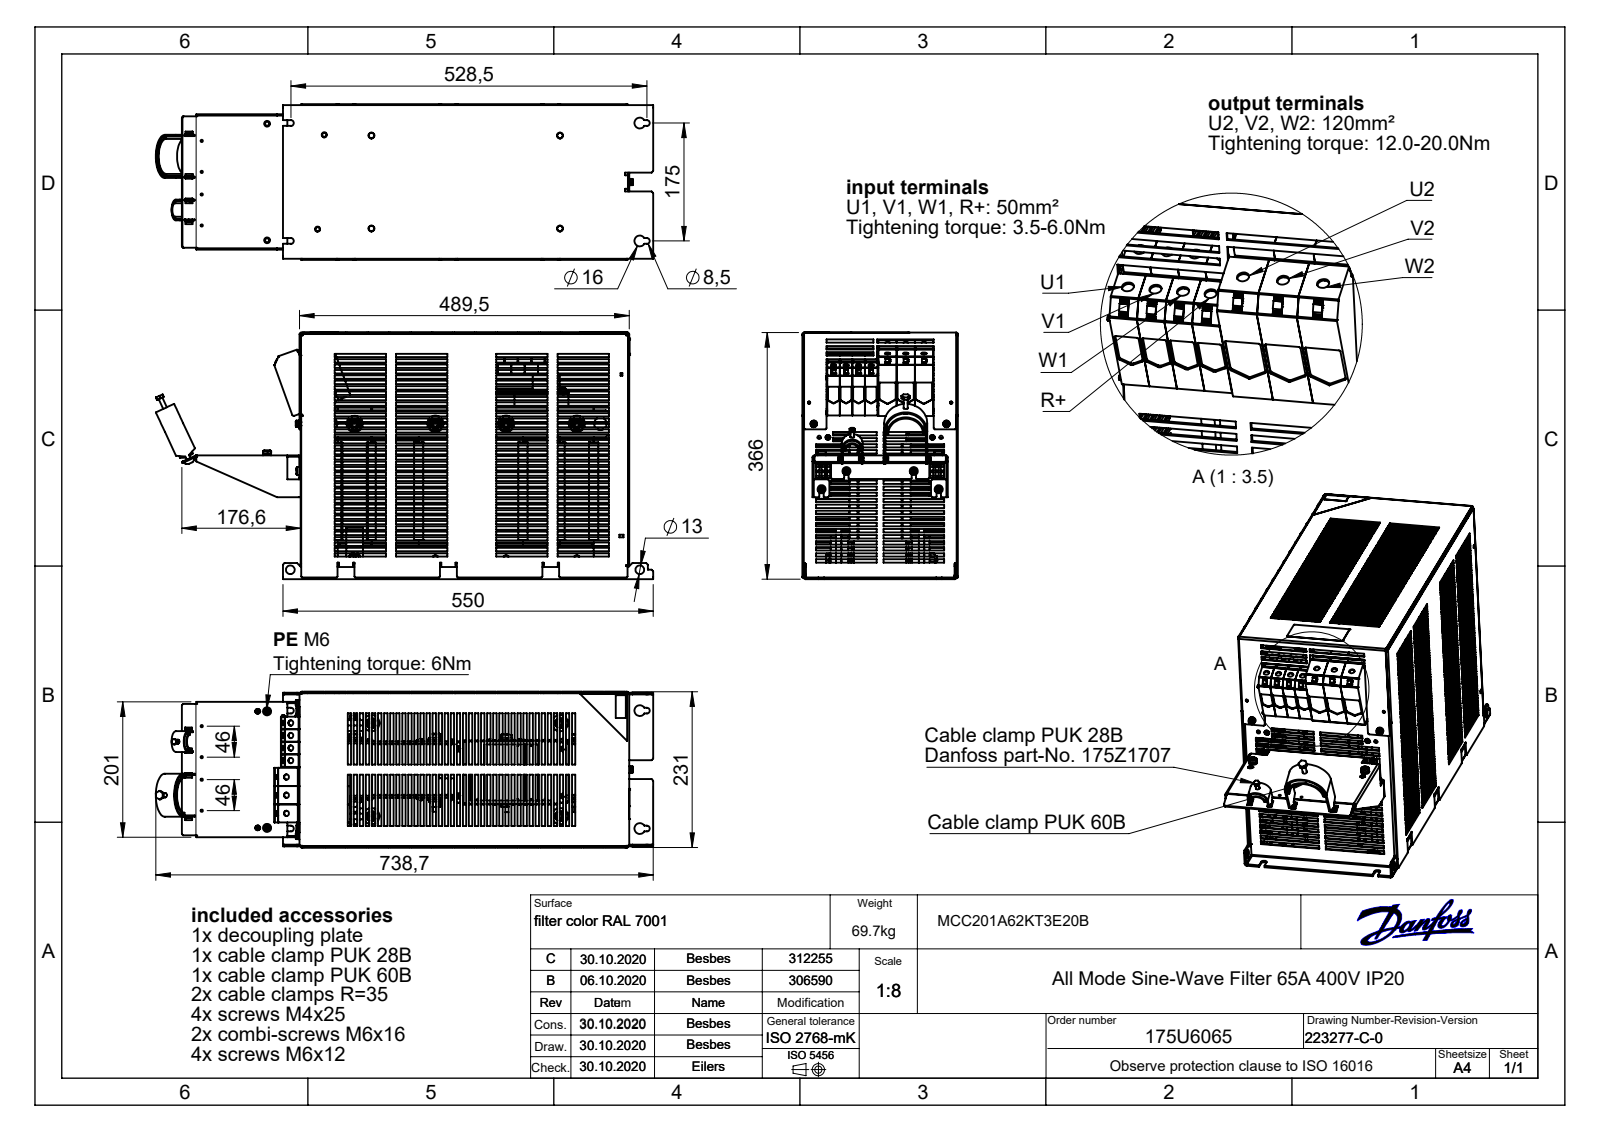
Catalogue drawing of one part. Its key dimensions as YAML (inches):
part_name: "200603 65A STEP; 139289; 128728; PEM Bolzen FH M6x15 10.9 vz_PEM Bolzen FH M6x15 10.9 vz (+8 more)"
step_written_by: "SolidWorks 2018 (AUTOMOTIVE_DESIGN)"
units: inches
bodies: {solids: 162, faces: 7219, planar: 5284, cylindrical: 1307, other: 628}
overall_size: [29.082, 14.413, 9.094]
volume: 790.9
surface_area: 5327
round_holes:
  - {diameter: 0.315, count: 23}
  - {diameter: 0.197, count: 14}
  - {diameter: 0.268, count: 12}
  - {diameter: 0.138, count: 10}
  - {diameter: 0.13, count: 8}
  - {diameter: 0.323, count: 8}
  - {diameter: 0.433, count: 8}
  - {diameter: 0.165, count: 7}
  - {diameter: 0.177, count: 7}
  - {diameter: 0.313, count: 7}
  - {diameter: 0.512, count: 7}
  - {diameter: 0.126, count: 6}
round_bosses_or_shafts:
  - {diameter: 0.039, count: 20}
  - {diameter: 0.315, count: 15}
  - {diameter: 0.63, count: 12}
  - {diameter: 0.709, count: 8}
  - {diameter: 0.394, count: 8}
  - {diameter: 0.236, count: 7}
  - {diameter: 0.472, count: 6}
  - {diameter: 0.945, count: 5}
partial_cylinders:
  - {radius: 0.039, count: 84}
  - {radius: 0.012, count: 34}
  - {radius: 0.035, count: 28}
  - {radius: 0.217, count: 22}
  - {radius: 0.079, count: 20}
  - {radius: 0.118, count: 19}
  - {radius: 0.394, count: 19}
  - {radius: 0.276, count: 16}
face_to_face_distances: [0.059, 3.012, 6.024, 2.953, 3.071, 9.035, 5.965, 6.083, 0.118, 0.079]
hole_center_spacings: [0.732, 1.519, 1.063, 1.331, 1.465, 1.979, 2.066, 4.134]
